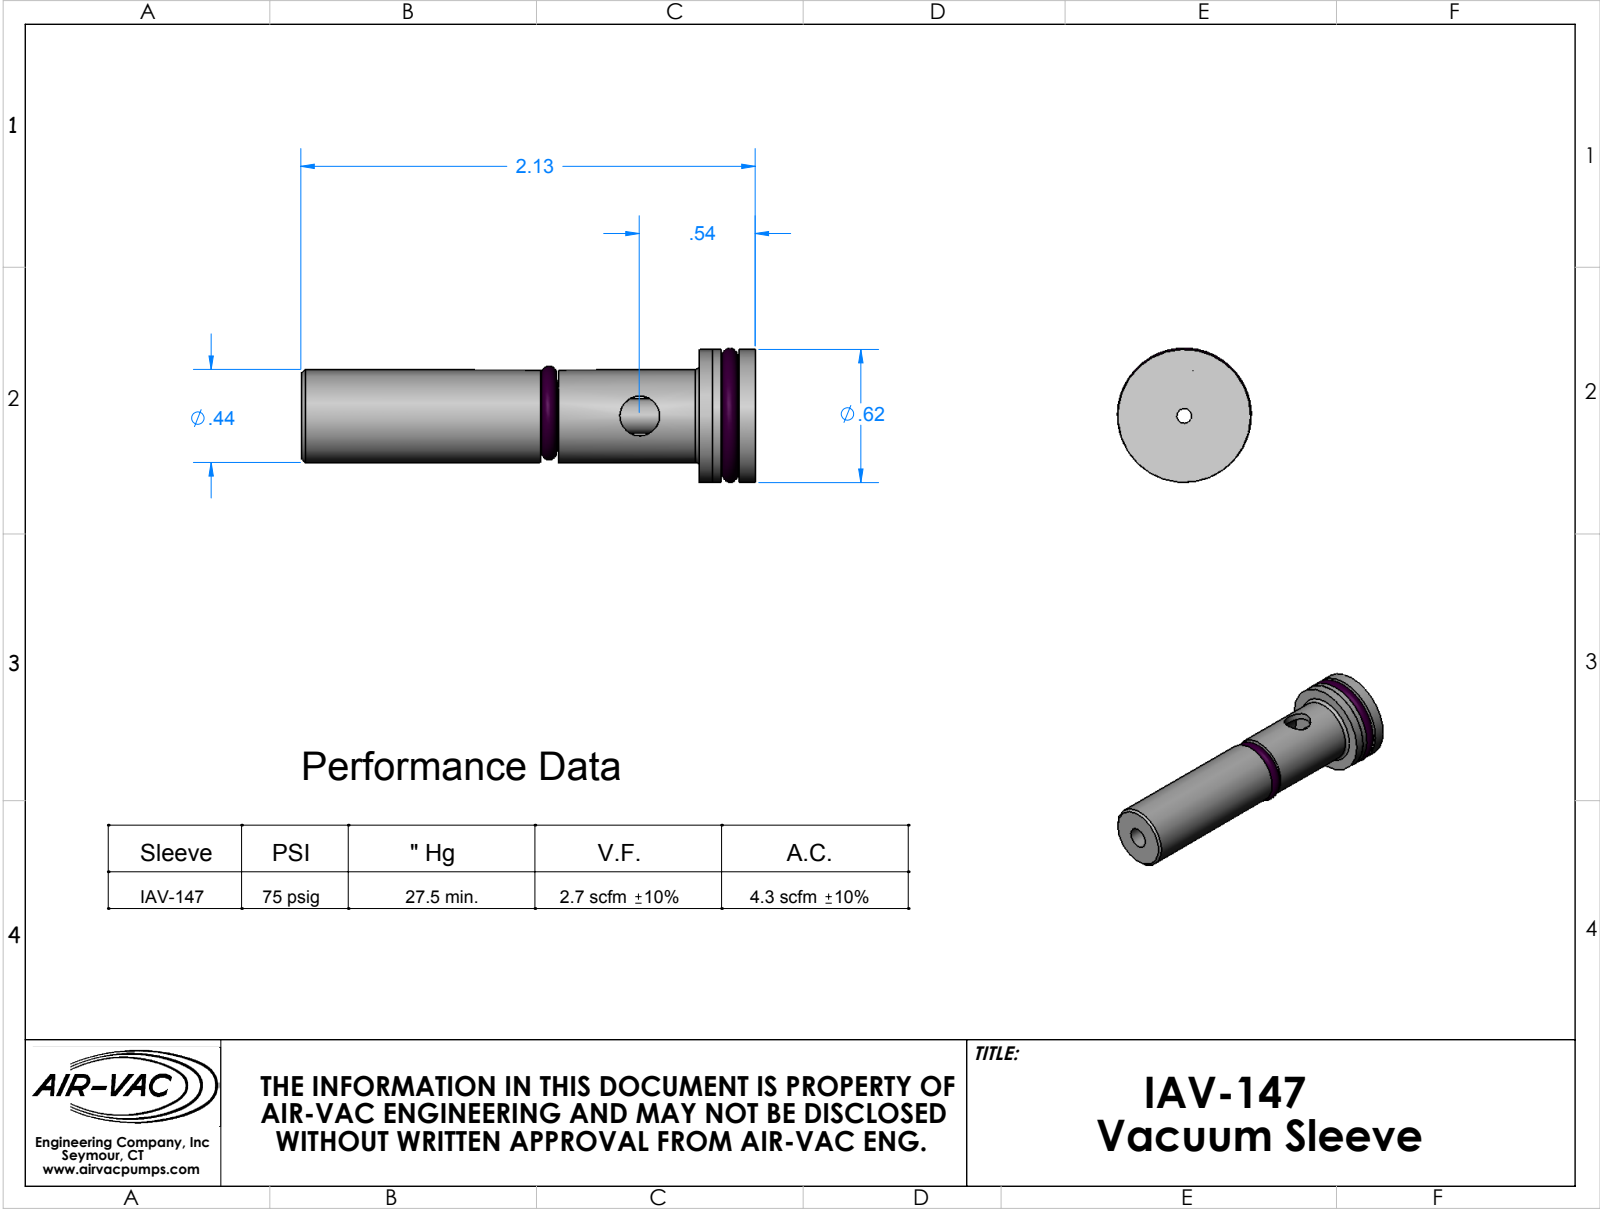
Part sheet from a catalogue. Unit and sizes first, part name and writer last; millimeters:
Units: millimetres
Overall size (bounding box): 54.1 × 16 × 16
Round holes (diameter × count): ⌀1.8 ×1, ⌀3.7 ×1, ⌀4.7 ×1, ⌀8.9 ×1
Round bosses / shafts (diameter × count): ⌀15.8 ×1, ⌀13.2 ×1, ⌀11.1 ×1, ⌀8.9 ×1, ⌀8.4 ×1, ⌀4.2 ×1
Main face-to-face distances: 5.1, 2.2, 6.7, 1.6, 21.5, 54.1, 49, 47.4, 4.1, 1
Volume: 4 930 mm³ · Surface area: 4 388 mm²
Bodies: 4 solids, 66 faces (12 planar, 28 cylindrical, 26 other)
Part name (STEP PRODUCT): IAV-147; IAV-147E_Web Model; IAV-147G_Web Model; 2-11-BUNA 70 (+1 more)
STEP written by: SolidWorks 2008 (AUTOMOTIVE_DESIGN)
